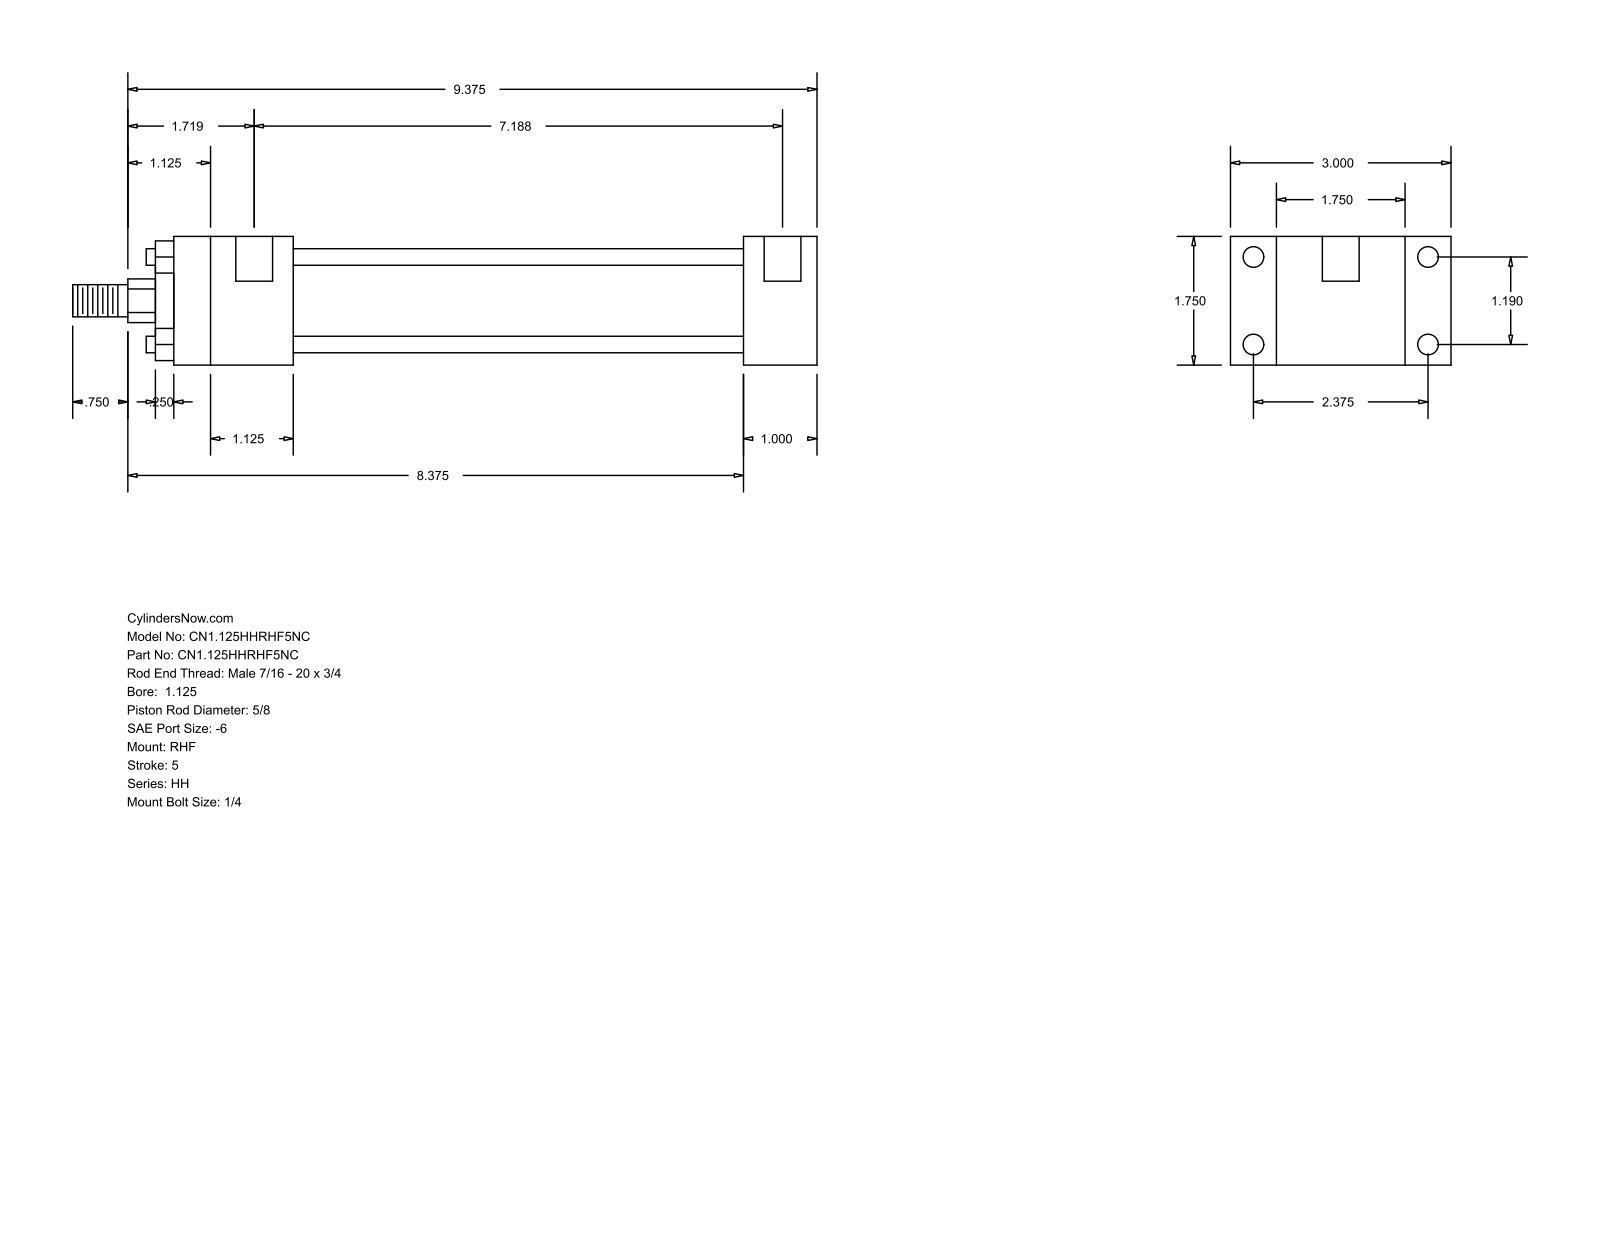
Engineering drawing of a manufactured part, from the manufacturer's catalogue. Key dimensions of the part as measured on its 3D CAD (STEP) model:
Part name (STEP PRODUCT): HH_RHF__0112_0.625
STEP written by: GSSL Pune (CONFIG_CONTROL_DESIGN)
Units: millimetres
Bodies: 0 solids, 88 faces (60 planar, 28 cylindrical, 0 other)
Overall size (bounding box): 257.18 × 76.2 × 44.45
Round holes (diameter × count): ⌀5.56 ×4, ⌀7.14 ×4, ⌀12.7 ×2
Round bosses / shafts (diameter × count): ⌀5.71 ×4, ⌀34.92 ×1, ⌀28.57 ×1, ⌀15.88 ×1, ⌀11.11 ×1
Partial cylindrical surfaces — rounded edges, fillets, slot ends (radius × count): R7.54 ×1
Main face-to-face distances: 44.46, 15.87, 25.4, 60.33, 76.2, 155.57, 180.97, 41.27, 196.84, 222.24
Hole centre spacings: 30.22, 60.32, 67.47, 179.39, 3.17, 182.56
